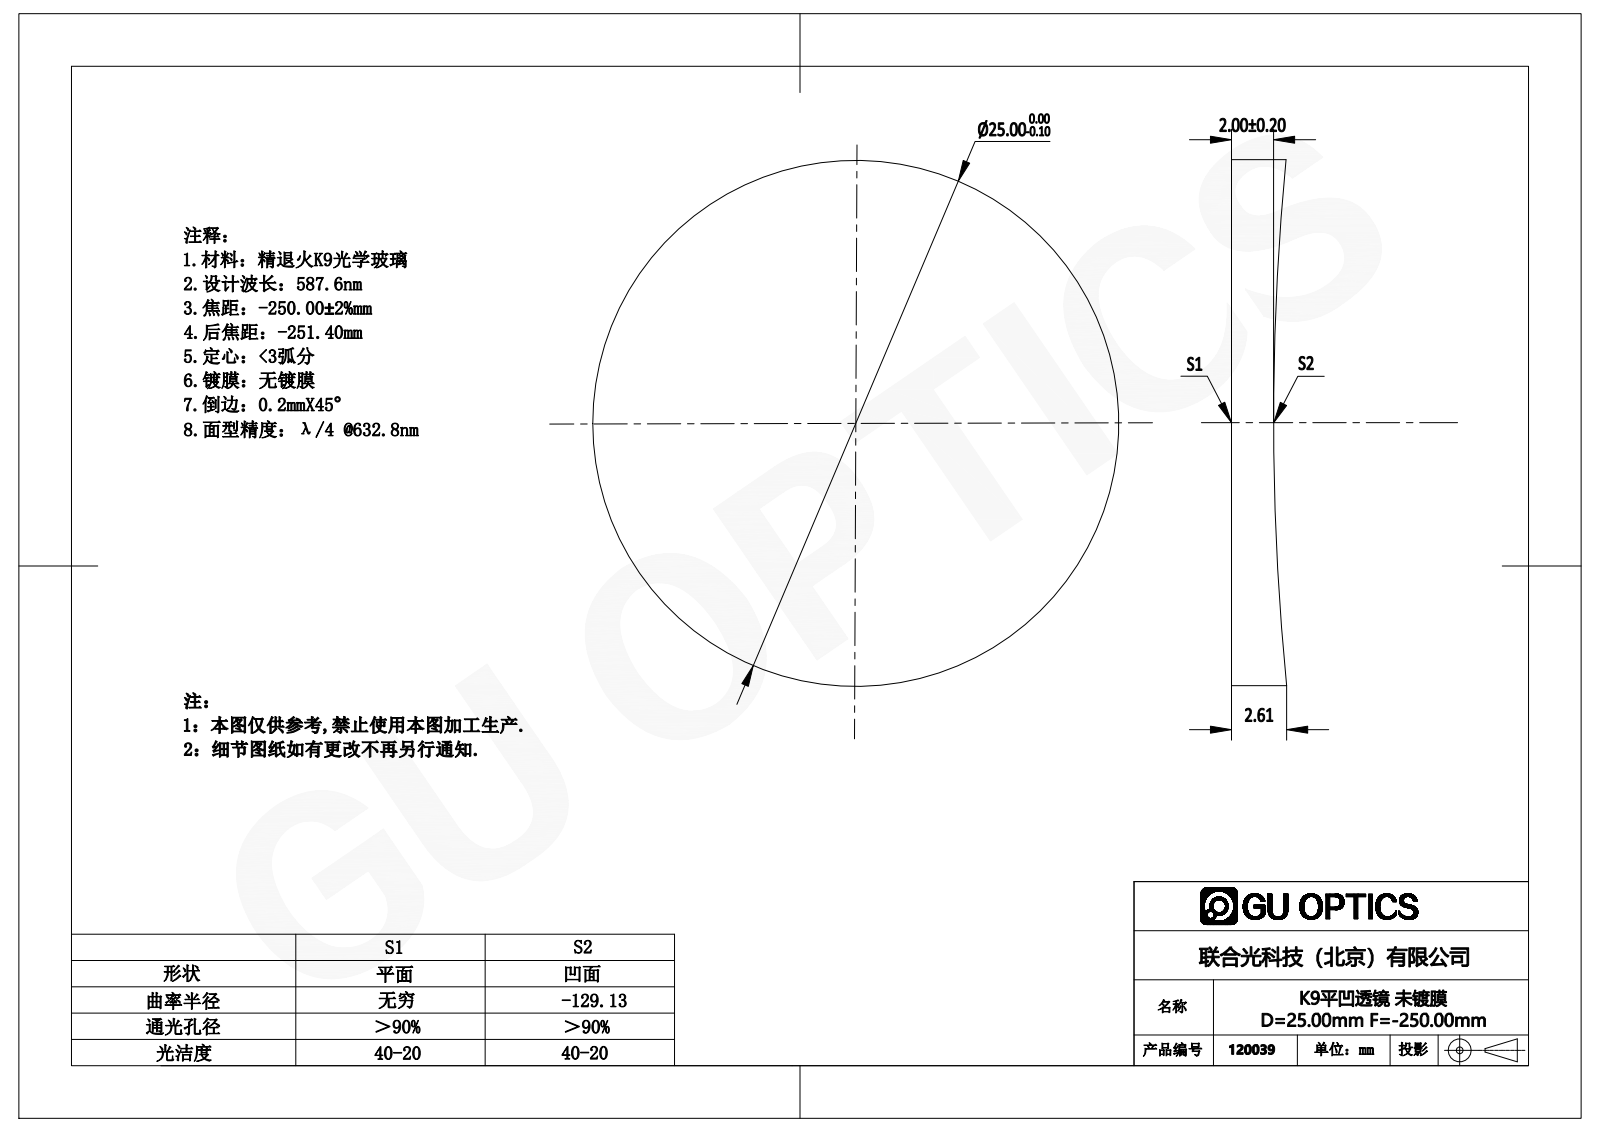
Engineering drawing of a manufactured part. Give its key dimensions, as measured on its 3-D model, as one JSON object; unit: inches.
{"part_name": "120039", "step_written_by": "SolidWorks 2016 (AUTOMOTIVE_DESIGN)", "units": "inches", "bodies": {"solids": 1, "faces": 5, "planar": 1, "cylindrical": 2, "other": 2}, "overall_size": [0.984, 0.984, 0.102], "volume_in3": 0.069, "surface_area_in2": 1.838, "round_bosses_or_shafts": [[0.984, 1]]}
